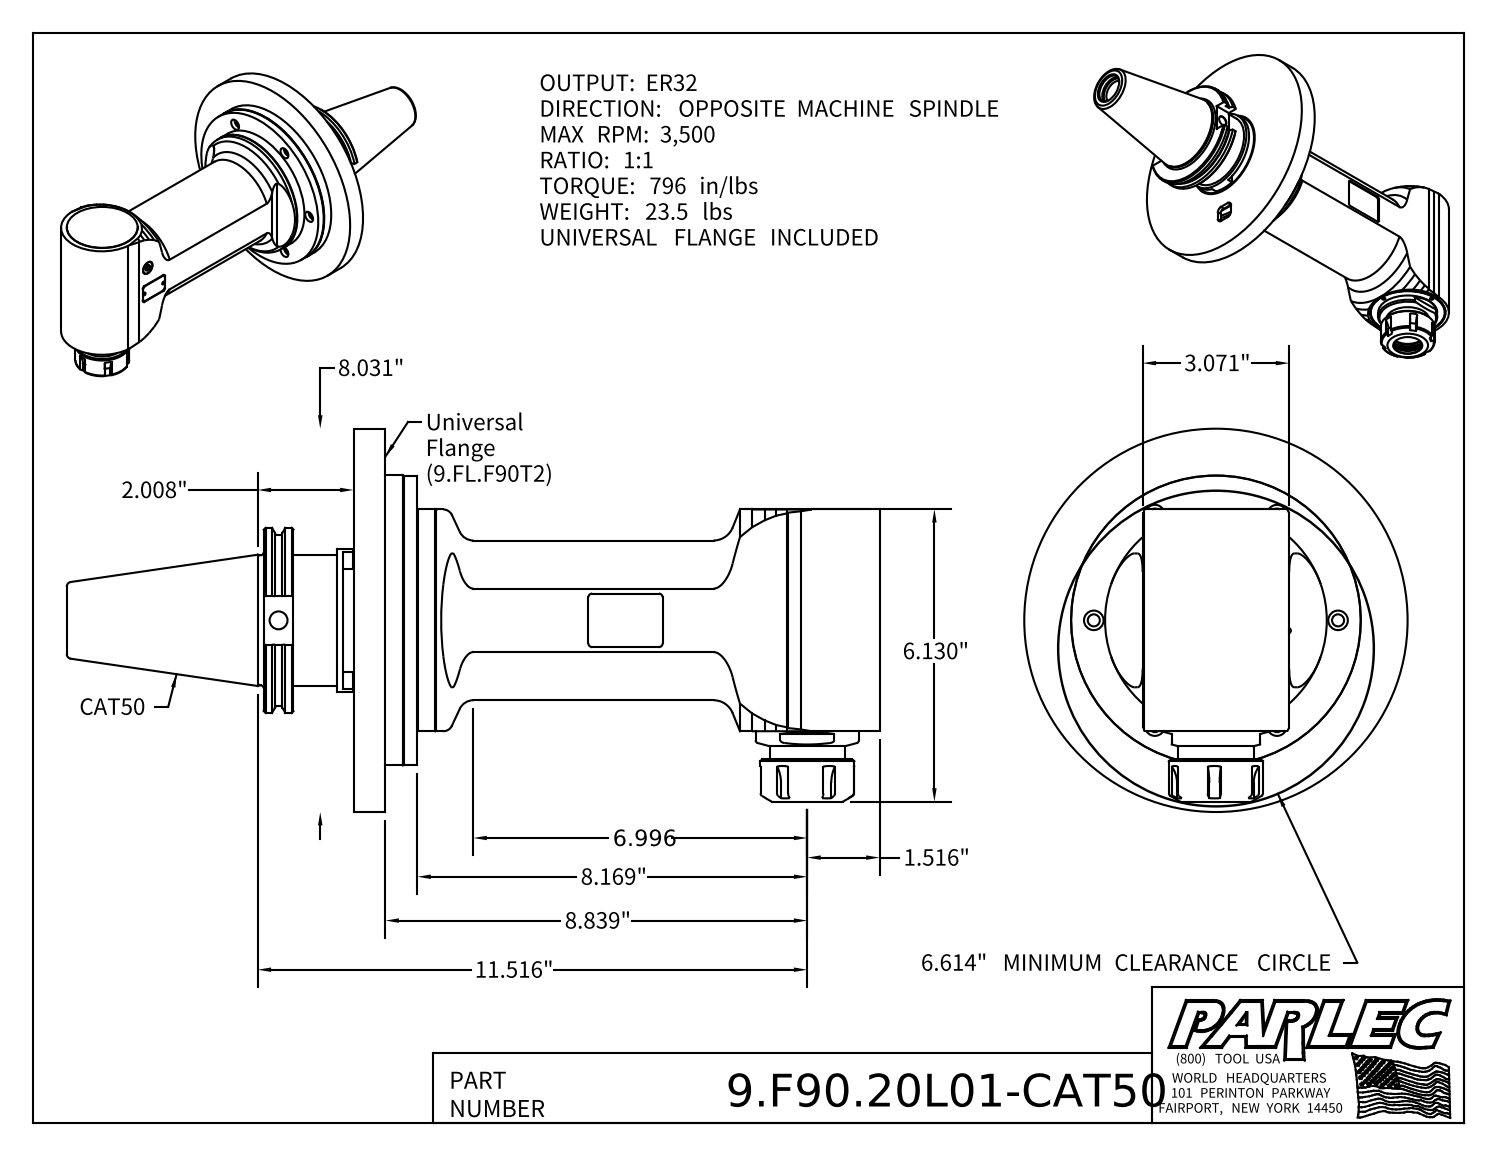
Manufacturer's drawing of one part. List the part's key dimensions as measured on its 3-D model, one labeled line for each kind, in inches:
Part name (STEP PRODUCT): 9.F90.20L01-CAT50; 9_F90_20L01; 9_SK_45_2 (Cat50, MTC); 9_FL_F90T2 (MTC, Universal Flange, Type 2)
STEP written by: Autodesk Inventor 2022 (AUTOMOTIVE_DESIGN)
Units: inches
Bodies: 5 solids, 368 faces (166 planar, 106 cylindrical, 96 other)
Overall size (bounding box): 17.031 × 8.031 × 8.031
Volume: 180 in³ · Surface area: 488.2 in²
Round holes (diameter × count): ⌀0.409 ×10, ⌀0.252 ×6, ⌀0.126 ×4, ⌀0.375 ×1, ⌀0.492 ×1, ⌀0.787 ×1, ⌀0.865 ×1, ⌀0.945 ×1, ⌀1.031 ×1, ⌀1.055 ×1, ⌀1.063 ×1, ⌀1.161 ×1
Round bosses / shafts (diameter × count): ⌀0.394 ×4, ⌀0.236 ×4, ⌀0.098 ×2, ⌀8.031 ×1, ⌀6.071 ×1, ⌀6.063 ×1, ⌀4.78 ×1, ⌀4.646 ×1
Partial cylindrical surfaces — rounded edges, fillets, slot ends (radius × count): R0.079 ×12, R0.157 ×6, R0.591 ×6, R1.496 ×1, R1.673 ×1
Main face-to-face distances: 0.669, 1.339, 3.071, 0.138, 0.531, 1.201, 0.354, 0.886, 0.217, 1.555
Hole centre spacings: 2.559, 0.857, 1.24, 1.754, 1.929, 2.559, 2.778, 3.581
